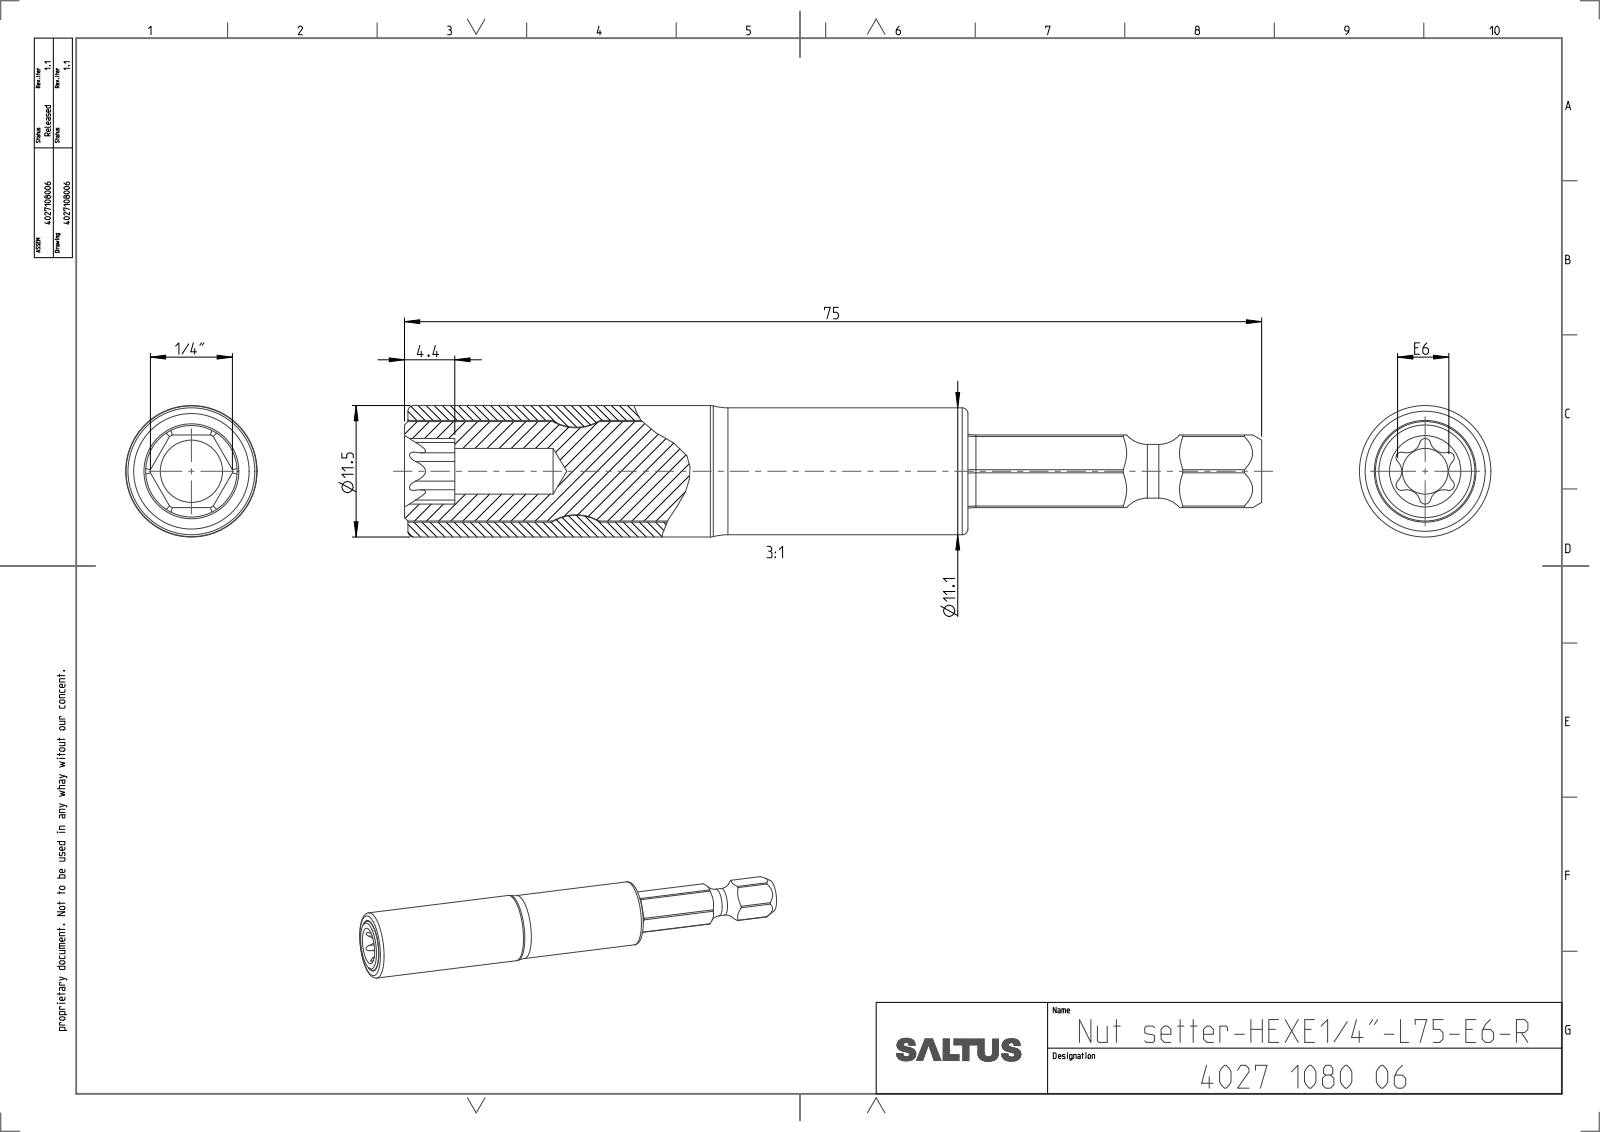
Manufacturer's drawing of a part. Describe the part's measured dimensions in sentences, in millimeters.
The part is named "4027911288; 4027299450; 4027108006_ASM". Its 3-D file was written by "CREO PARAMETRIC BY PTC INC, 2022414 (CONFIG_CONTROL_DESIGN)". It is 2 solids with 103 faces: 17 planar, 50 cylindrical and 36 other. Overall it measures 75 by 11.5 by 11.5 millimeters. Its volume is 5 395 cubic millimeters and its surface area 5 233 square millimeters. Round holes: 1 of diameter 4, 1 of diameter 8.3, 1 of diameter 8.9. Round bosses or shafts: 1 of diameter 11.5, 1 of diameter 11.1, 1 of diameter 8.7, 1 of diameter 8, 1 of diameter 4.7. Partial cylindrical surfaces (rounded edges, fillets, slot ends): 6 of radius 0.48, 6 of radius 1.22, 6 of radius 5, 1 of radius 3.59. The main face-to-face distances are 6.34, 6.36, 49, 25.7, 74.7, 75, 49.3, 70.6, 44.9, 4.1.
